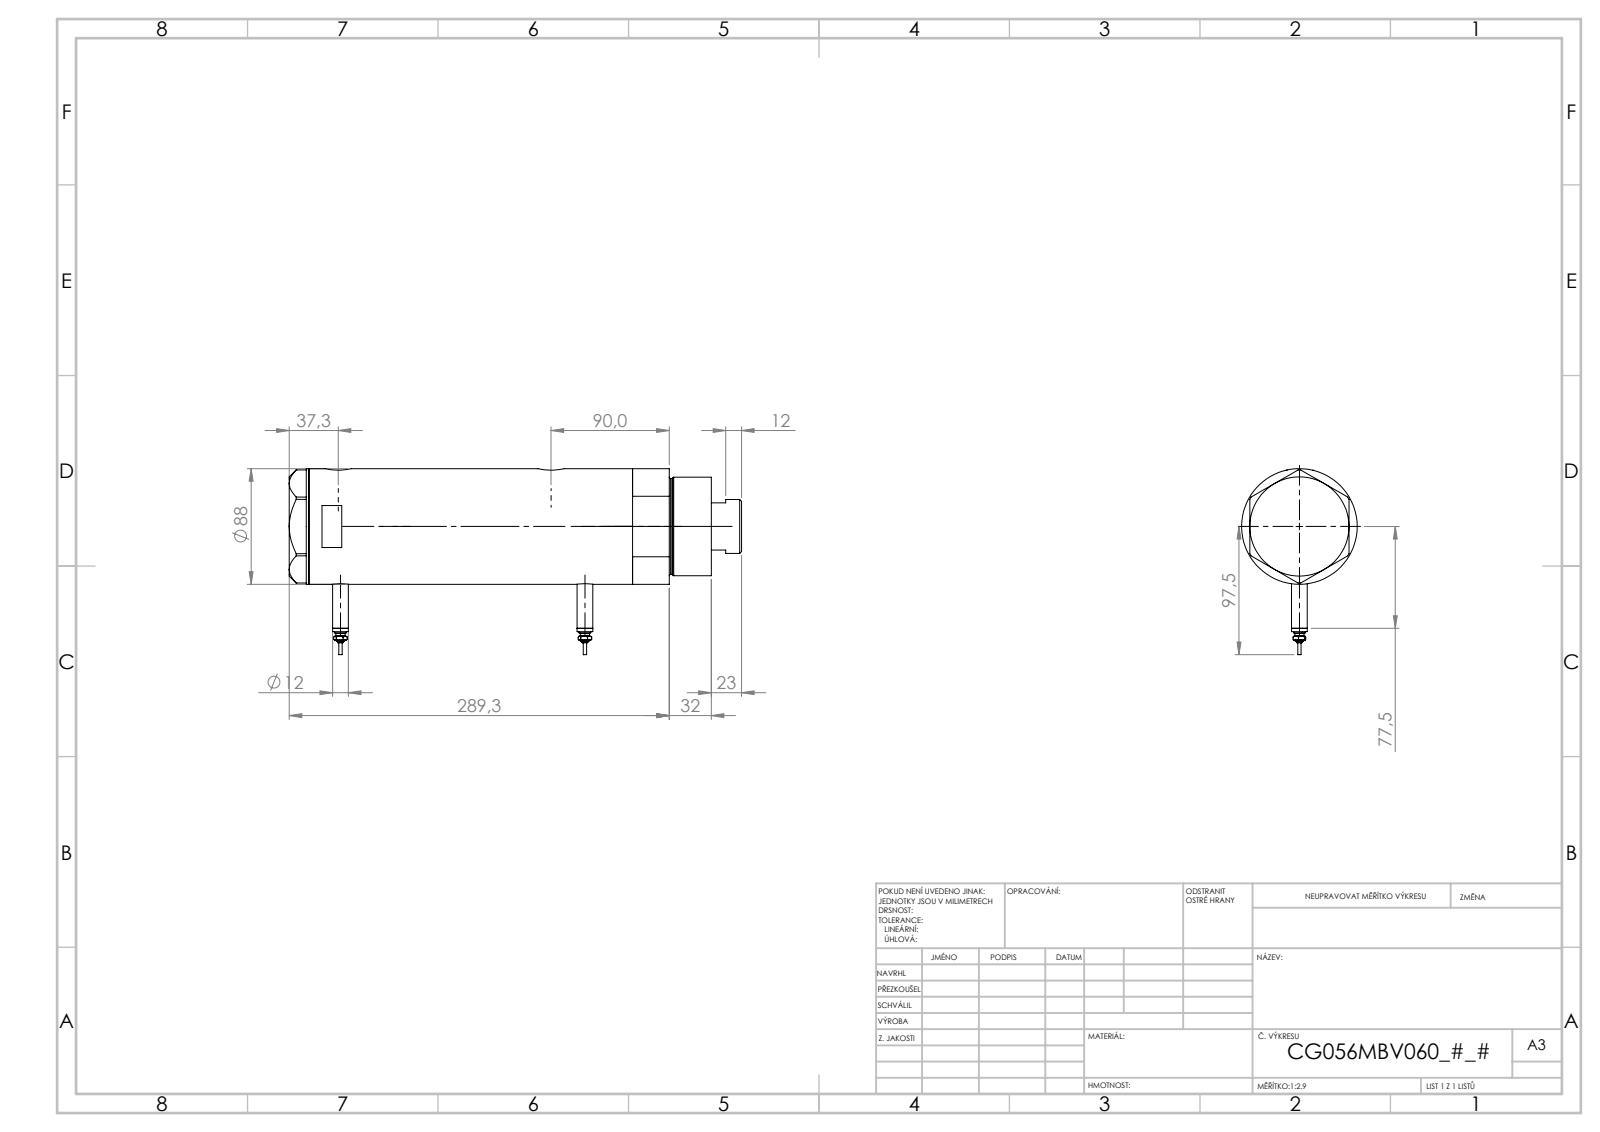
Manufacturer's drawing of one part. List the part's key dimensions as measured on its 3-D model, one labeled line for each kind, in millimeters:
Part name (STEP PRODUCT): V270CG_FRONT; V270CG_MIDDLE; V270CG_BACK; Switch (+1 more)
STEP written by: SolidWorks 2019 (CONFIG_CONTROL_DESIGN)
Units: millimetres
Bodies: 6 solids, 213 faces (80 planar, 69 cylindrical, 64 other)
Overall size (bounding box): 344.3 × 141.5 × 88
Volume: 1 834 000 mm³ · Surface area: 255 565 mm²
Round holes (diameter × count): ⌀12.5 ×2, ⌀13.16 ×2, ⌀20 ×2, ⌀14.5 ×1, ⌀42 ×1, ⌀43.5 ×1, ⌀56 ×1, ⌀60 ×1, ⌀80 ×1
Round bosses / shafts (diameter × count): ⌀12 ×2, ⌀9 ×2, ⌀7 ×2, ⌀4.5 ×2, ⌀2.5 ×2, ⌀88 ×1, ⌀75 ×1, ⌀73 ×1
Main face-to-face distances: 184.4, 26, 158.4, 15, 41, 199.4, 306.3, 321.3, 280.3, 121.9
Hole centre spacings: 1.7, 25.8, 160.3, 162, 186.1, 187.8
